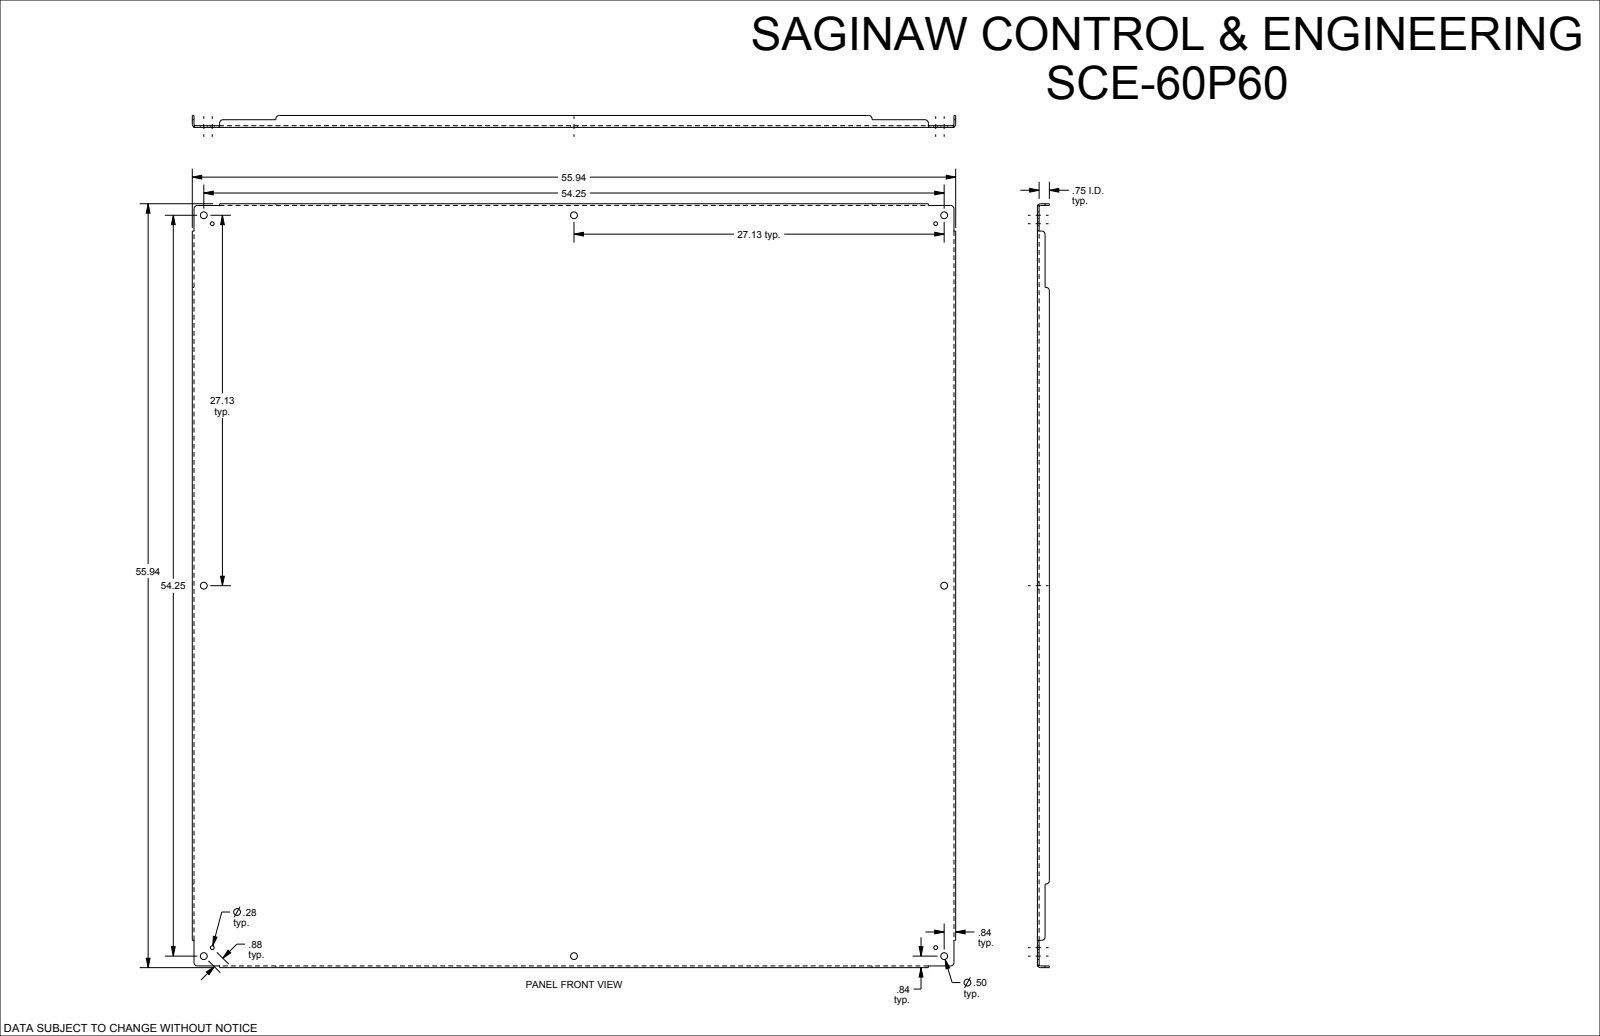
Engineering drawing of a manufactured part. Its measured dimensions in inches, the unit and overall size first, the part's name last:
Units: inches
Overall size (bounding box): 55.938 × 55.938 × 0.875
Round holes (diameter × count): ⌀0.5 ×8, ⌀0.281 ×4
Partial cylindrical surfaces — rounded edges, fillets, slot ends (radius × count): R0.25 ×12, R0.112 ×4, R0.237 ×4
Main face-to-face distances: 0.125, 0.125, 55.813, 55.687, 55.938, 0.75, 0.875, 0.312, 0.438, 0.563
Hole centre spacings: 26.513, 27.125, 53.635, 59.824, 60.653, 54.25, 0.875, 38.36
Volume: 406.9 in³ · Surface area: 6 540 in²
Bodies: 1 solid, 110 faces (46 planar, 40 cylindrical, 24 other)
Part name (STEP PRODUCT): SCE-60P60
STEP written by: SolidWorks 2019 (CONFIG_CONTROL_DESIGN)
